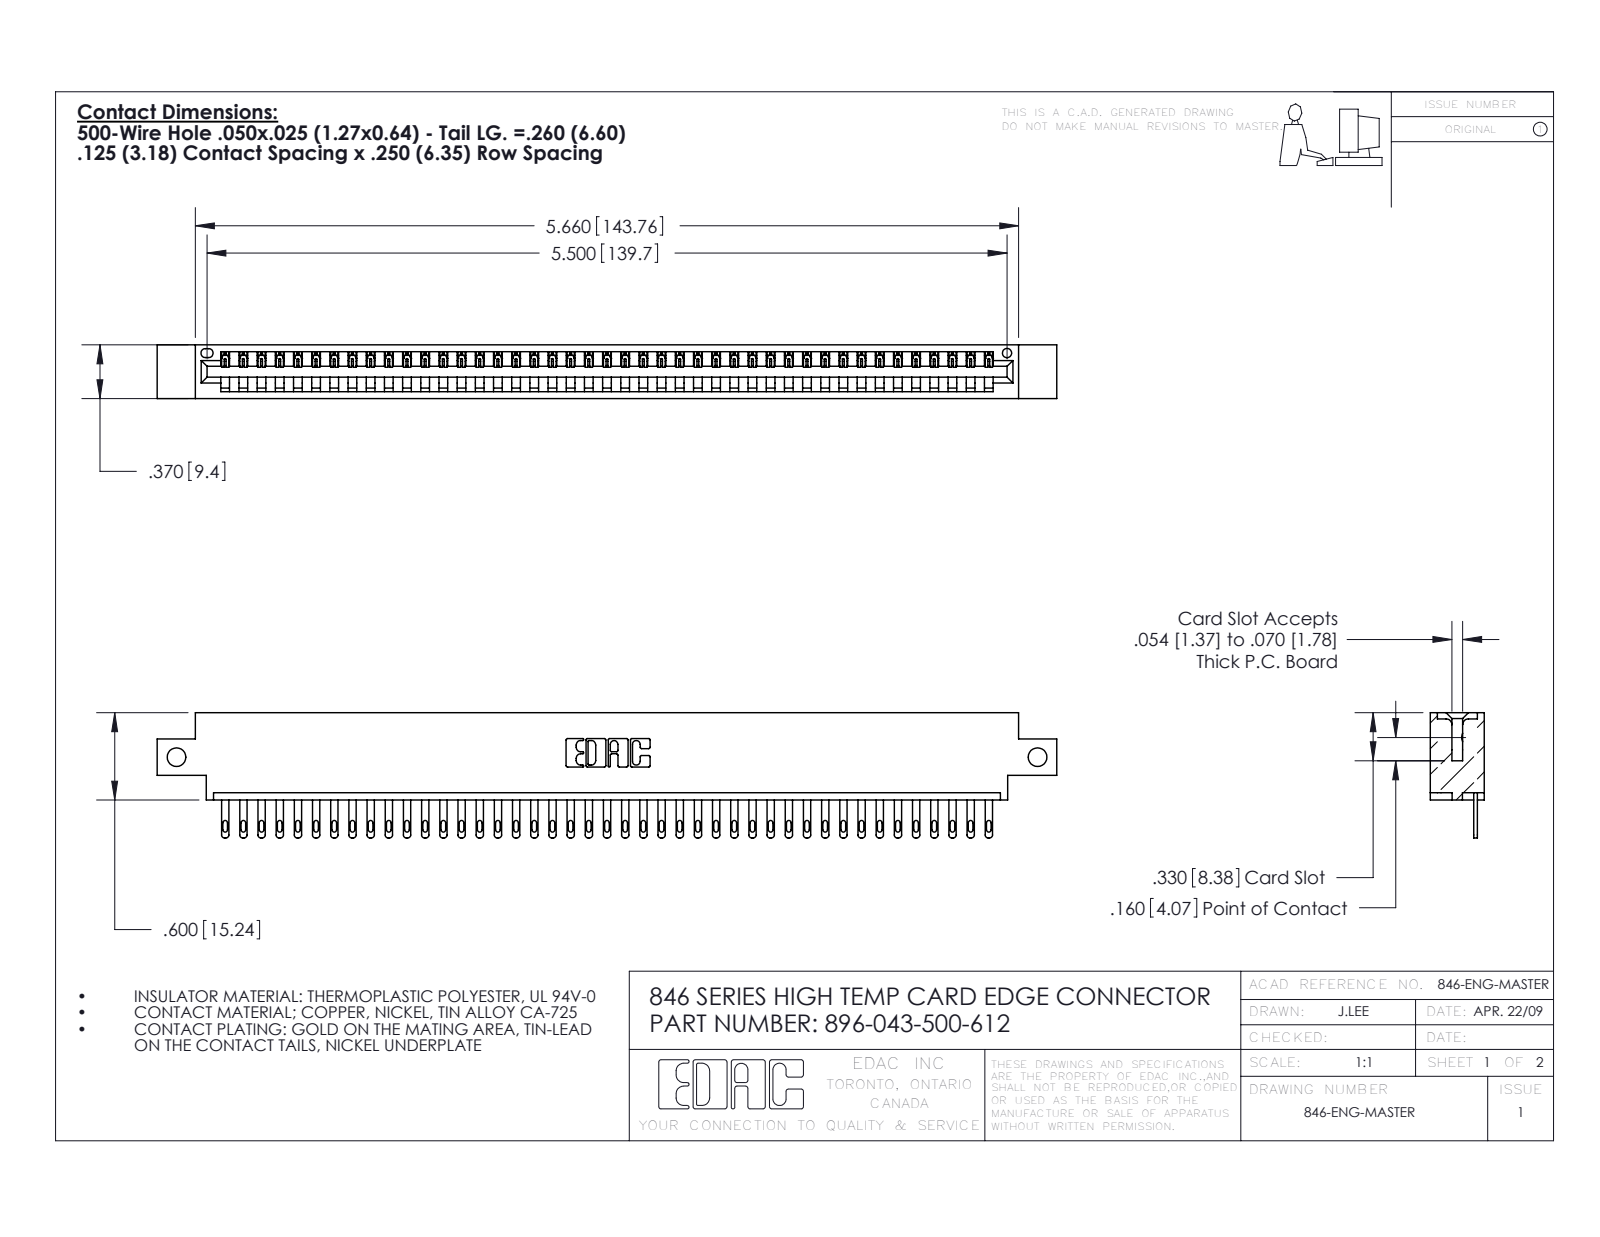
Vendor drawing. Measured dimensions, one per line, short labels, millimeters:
name: 896-043-500-612; 846 Part_0.170 Offset - Side Mount; 345-292-001_345-293-100
written by: SolidWorks 2020 (CONFIG_CONTROL_DESIGN)
unit: mm
bodies: 44 solids, 2448 faces (1542 planar, 906 cylindrical, 0 other)
size: 157.1 × 21.8 × 9.4
volume: 14 800 mm³; area: 18 660 mm²
holes: 2× ⌀3.3, 1× ⌀1.6
rounds: 86× R0.2, 86× R0.4, 86× R0.5, 22× R0.3, 6× R0.2, 6× R0.8, 3× R0.7, 2× R0.8
face distances: 1.2, 8.2, 9.4, 6.4, 1.8, 7.6, 0.6, 3.8, 5.6, 2.5
hole spacings: 150.4
